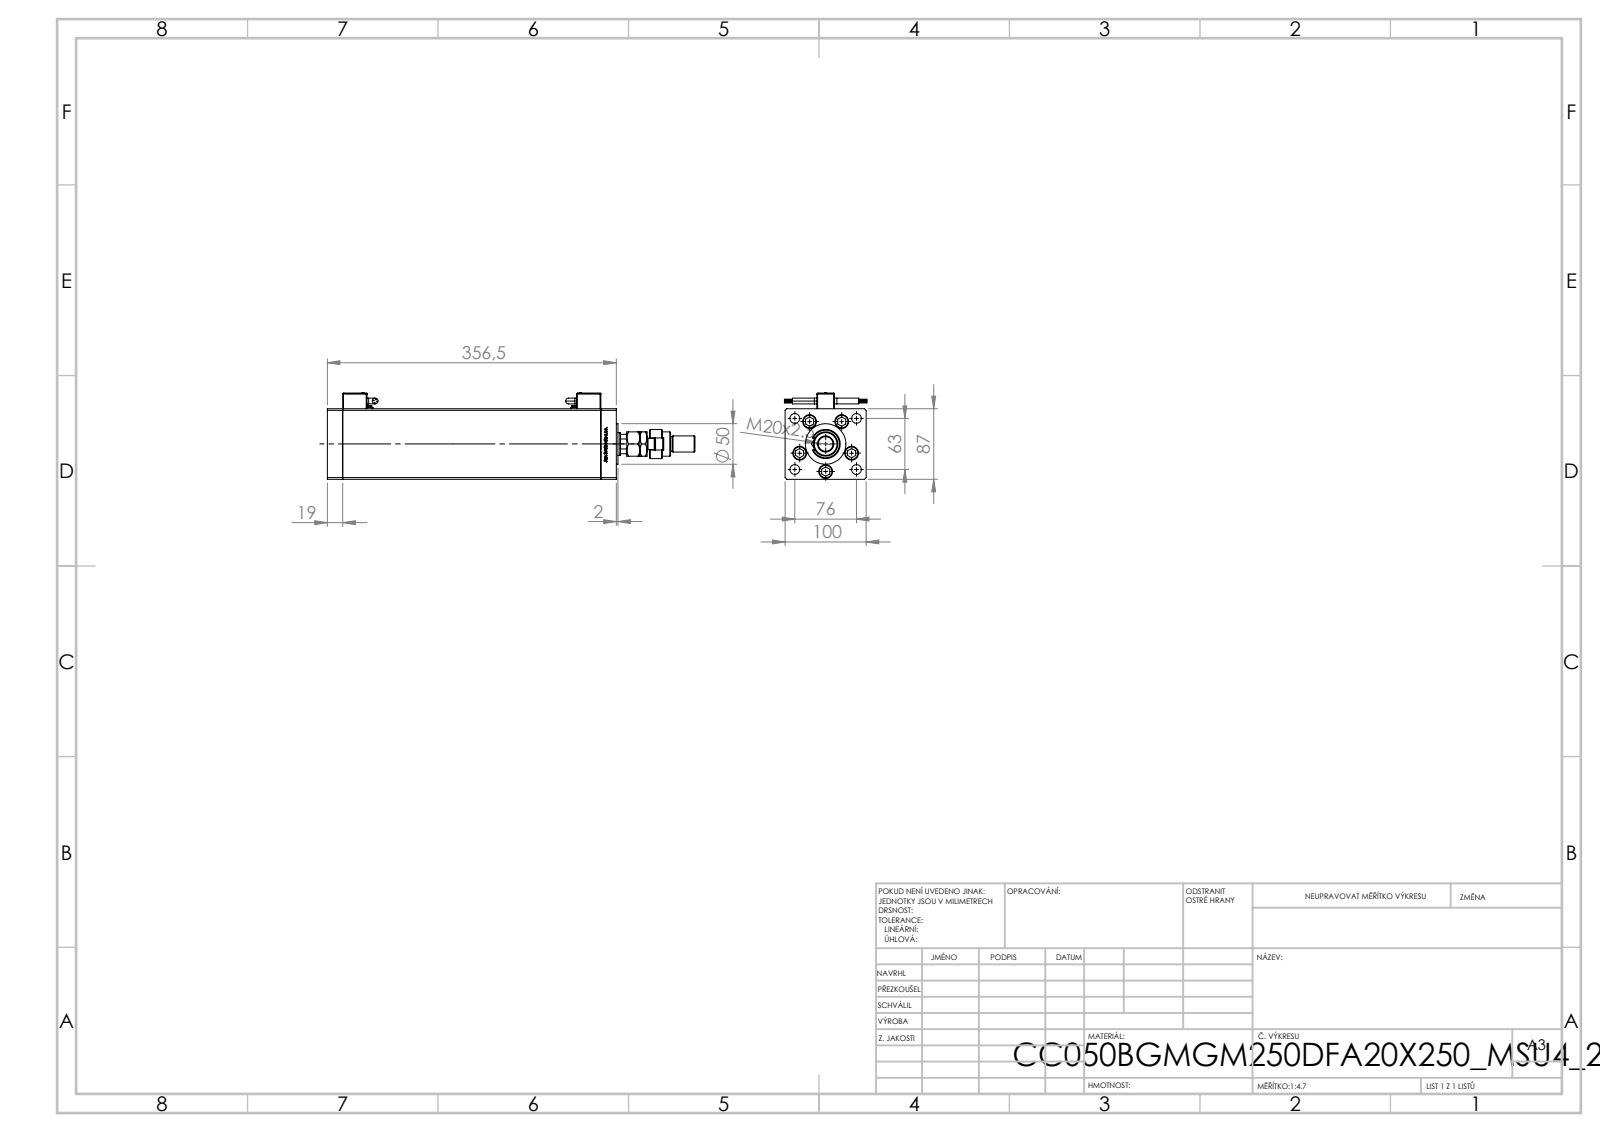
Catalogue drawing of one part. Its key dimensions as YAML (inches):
part_name: "MFA; V220C_B MIDDLE; V220C BACK_B; FEMALE_PART_FOR_DFA (+4 more)"
step_written_by: "SolidWorks 2019 (CONFIG_CONTROL_DESIGN)"
units: inches
bodies: {solids: 18, faces: 1472, planar: 568, cylindrical: 250, other: 654}
overall_size: [17.854, 4.217, 4]
volume: 166.8
surface_area: 524.7
round_holes:
  - {diameter: 0.531, count: 7}
  - {diameter: 0.669, count: 5}
  - {diameter: 0.472, count: 4}
  - {diameter: 0.079, count: 2}
  - {diameter: 0.142, count: 2}
  - {diameter: 0.197, count: 2}
  - {diameter: 0.276, count: 2}
  - {diameter: 0.518, count: 2}
  - {diameter: 0.728, count: 1}
  - {diameter: 1.102, count: 1}
round_bosses_or_shafts:
  - {diameter: 0.033, count: 8}
  - {diameter: 0.315, count: 5}
  - {diameter: 0.276, count: 4}
  - {diameter: 0.669, count: 2}
  - {diameter: 0.236, count: 2}
  - {diameter: 0.138, count: 2}
  - {diameter: 0.098, count: 2}
  - {diameter: 1.969, count: 1}
partial_cylinders:
  - {radius: 0.039, count: 24}
  - {radius: 0.157, count: 4}
  - {radius: 0.037, count: 2}
  - {radius: 0.295, count: 1}
  - {radius: 0.472, count: 1}
  - {radius: 0.531, count: 1}
face_to_face_distances: [3.937, 3.425, 0.748, 12.539, 13.287, 1.348, 14.035, 3.012, 0.413, 3.169]
hole_center_spacings: [1.339, 0.732, 1.561, 1.943, 2.281, 0.325, 0.828, 1.499]
